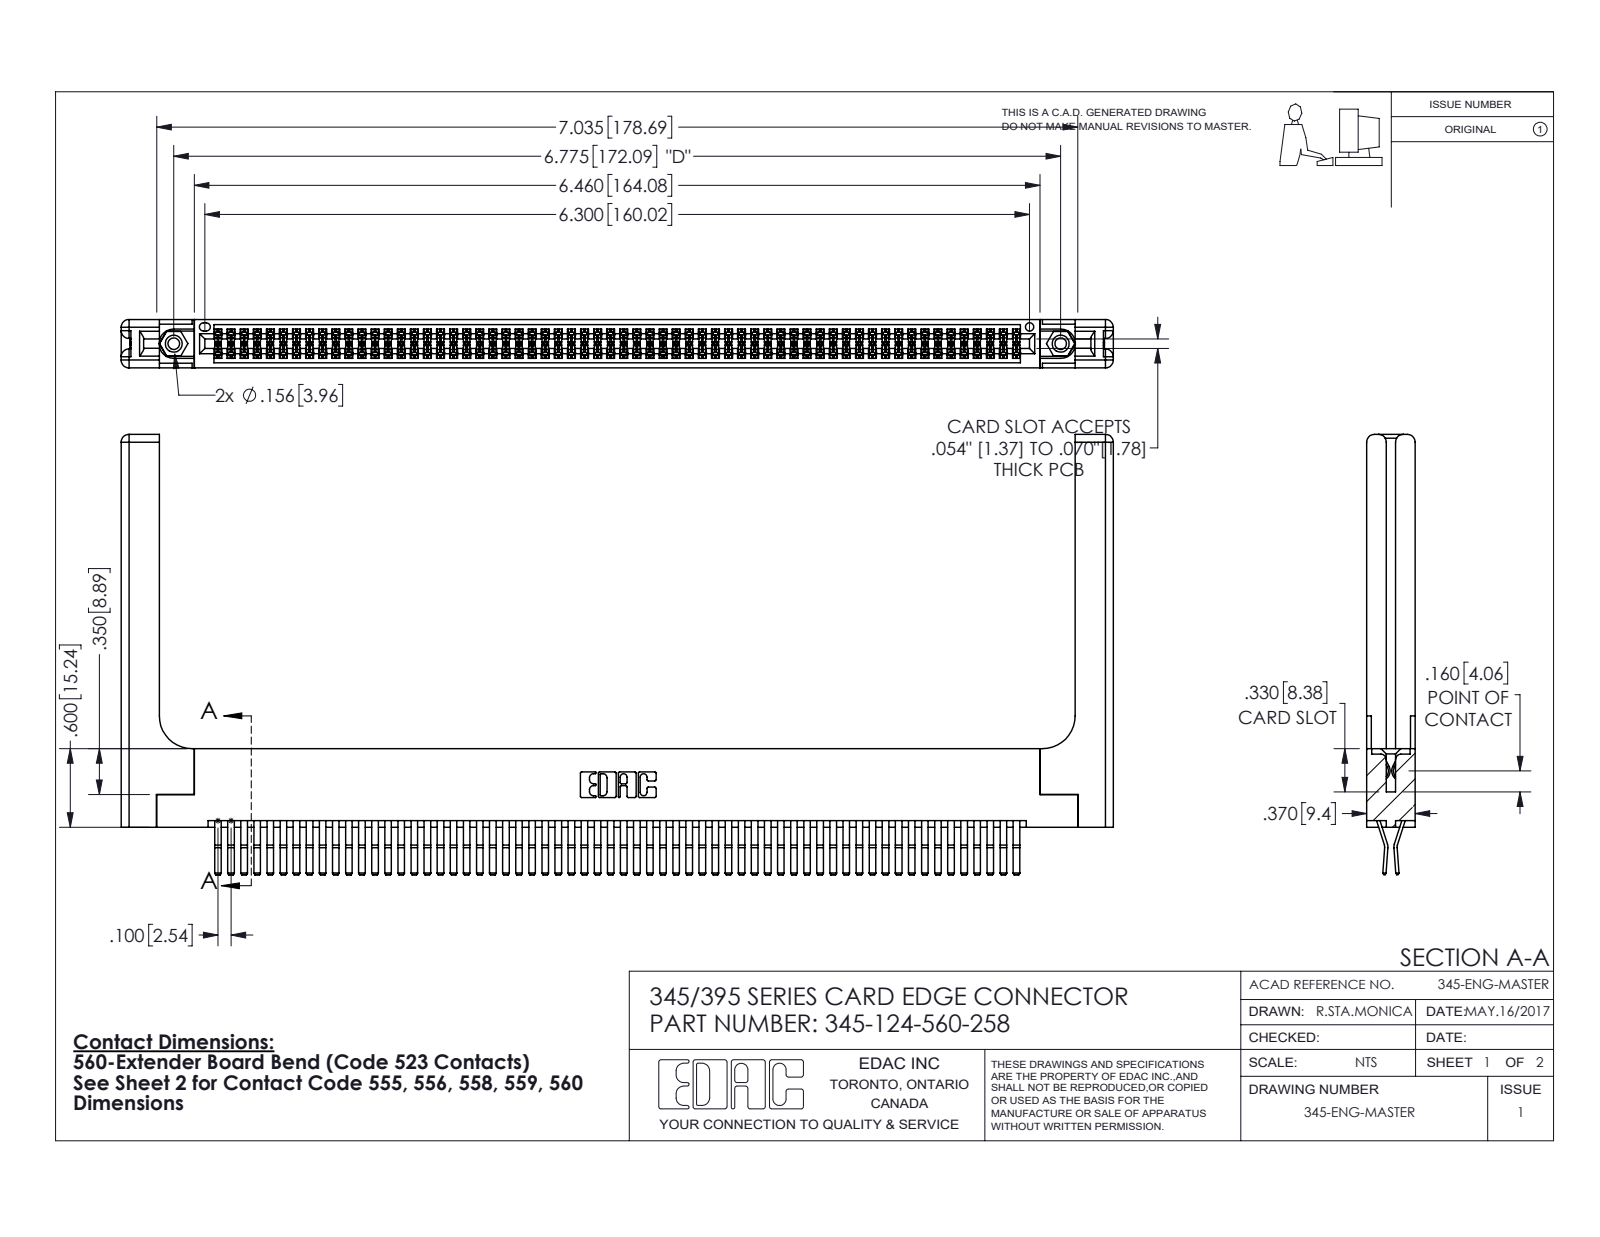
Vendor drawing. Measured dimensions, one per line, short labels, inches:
name: 345 Part_Flush Mounting Lugs - 0.156 Dia-TH; 345-124-560-258; 345-292-001_560 Tail; 345-220-058_345-220-058 (+1 more)
written by: SolidWorks 2016 (CONFIG_CONTROL_DESIGN)
unit: in
bodies: 129 solids, 6830 faces (4320 planar, 2450 cylindrical, 60 other)
size: 7.579 × 3.362 × 0.37
volume: 1.719 in³; area: 56.81 in²
holes: 2× ⌀0.089, 2× ⌀0.125, 2× ⌀0.156, 1× ⌀0.064
bosses: 2× ⌀0.155
rounds: 186× R0.006, 22× R0.01, 16× R0.06, 6× R0.007, 6× R0.031, 3× R0.026, 2× R0.01, 2× R0.014
face distances: 0.072, 0.298, 0.025, 0.37, 0.2, 0.098, 0.272, 0.225, 0.15, 0.148
hole spacings: 0.27, 6.539, 6.775
